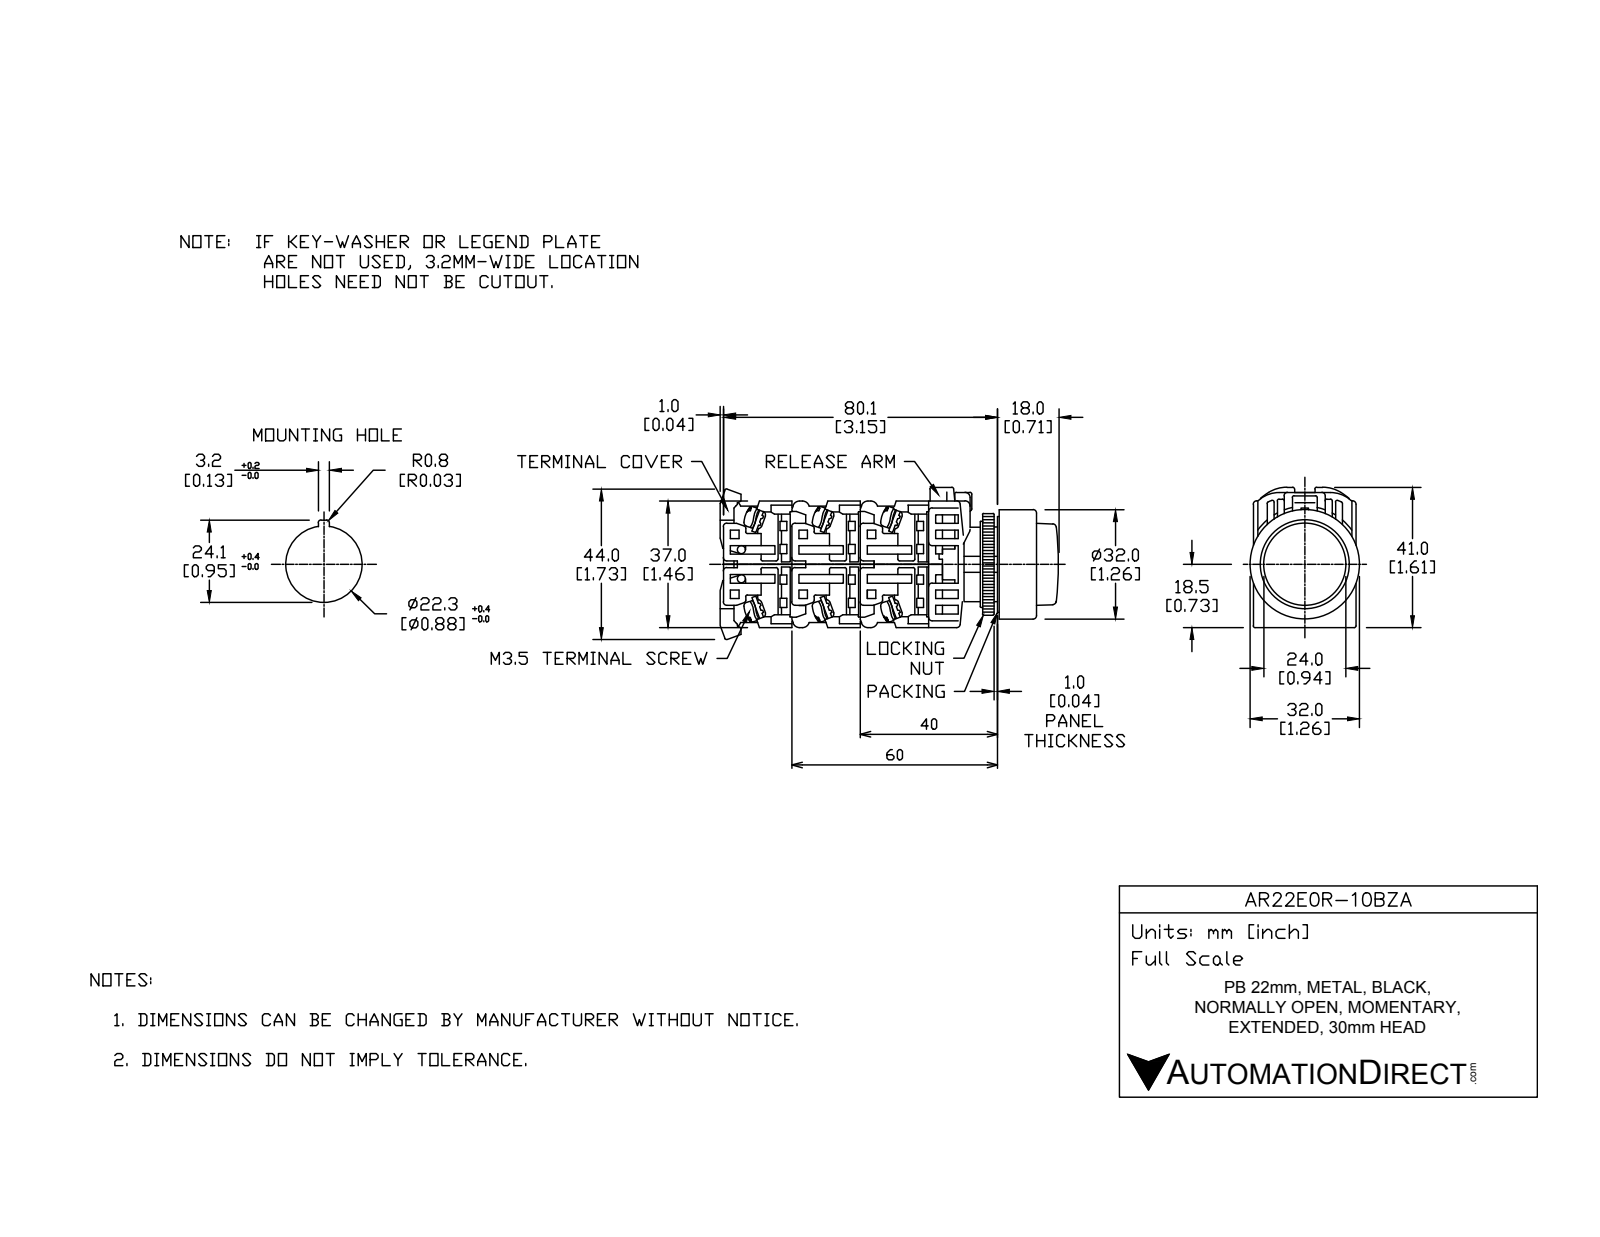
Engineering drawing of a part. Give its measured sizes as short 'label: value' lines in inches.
name: AR22E0R-10BZA
written by: SolidWorks 2017 (AUTOMOTIVE_DESIGN)
unit: in
bodies: 12 solids, 297 faces (201 planar, 74 cylindrical, 22 other)
size: 2.352 × 1.614 × 1.26
volume: 1.858 in³; area: 30.82 in²
holes: 1× ⌀0.858, 1× ⌀0.866, 1× ⌀0.984, 1× ⌀1.22
bosses: 2× ⌀0.197, 1× ⌀1.26, 1× ⌀1.201, 1× ⌀1.173, 1× ⌀0.945, 1× ⌀0.937, 1× ⌀0.856, 1× ⌀0.669
rounds: 23× R0.02, 4× R0.069, 4× R0.197, 2× R0.157, 1× R0.653, 1× R0.693
face distances: 0.039, 1.122, 0.709, 0.118, 0.079, 1.142, 1.181, 0.413, 0.315, 0.807
